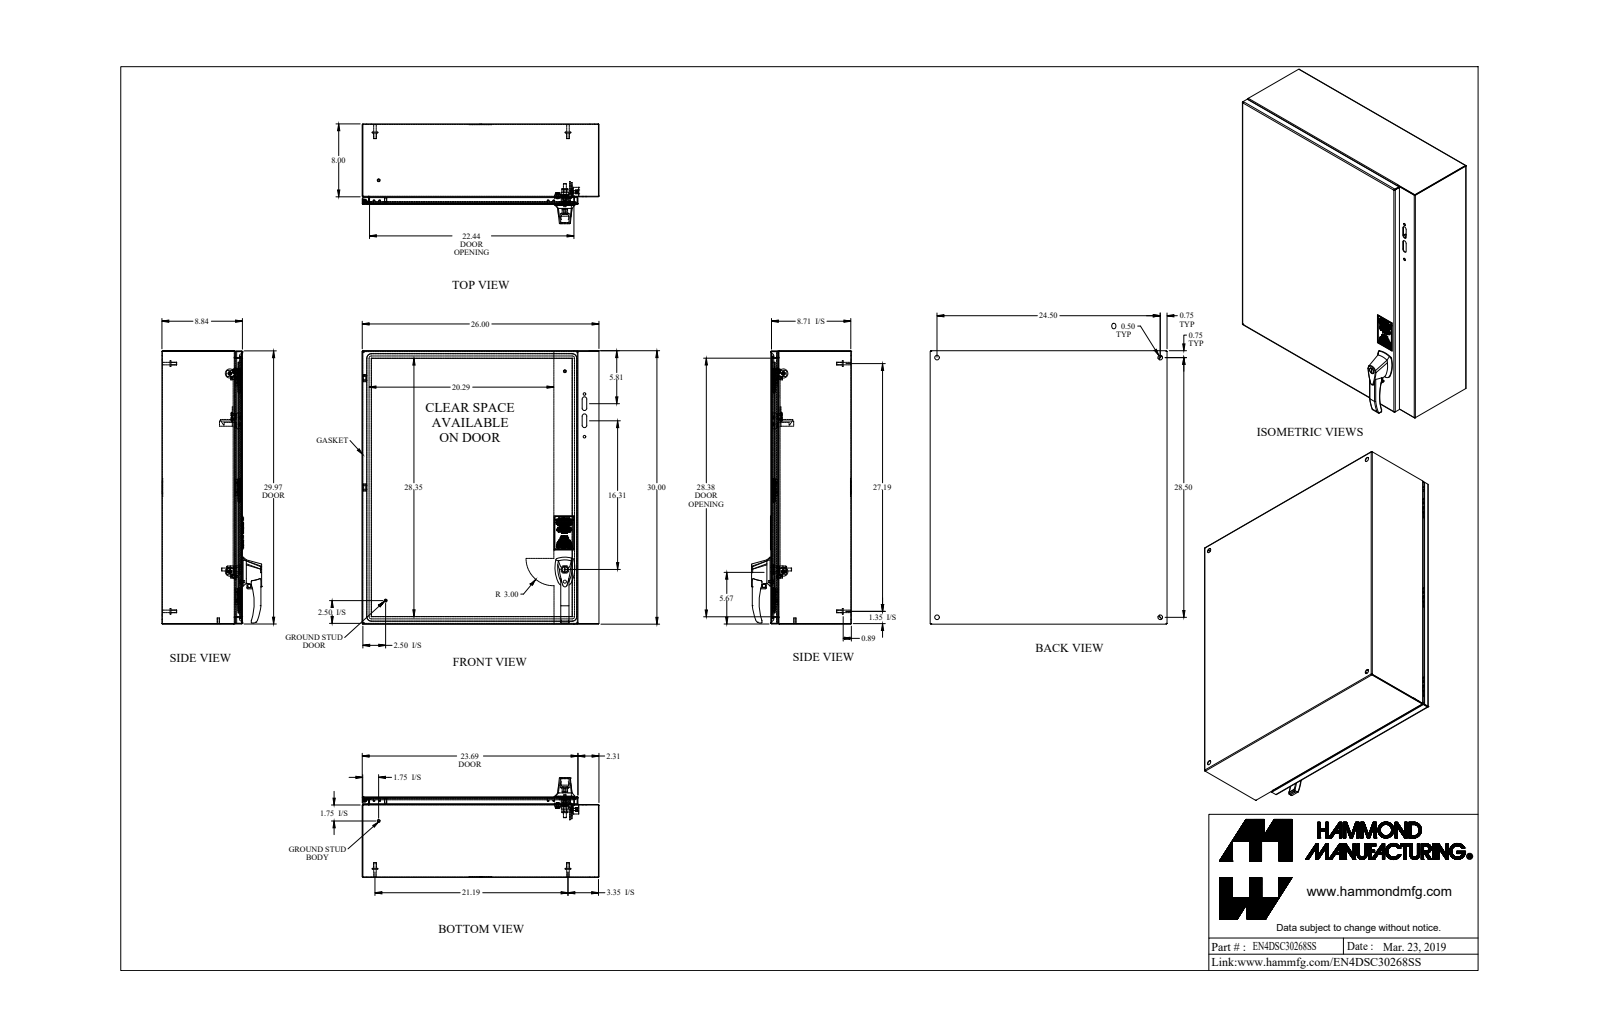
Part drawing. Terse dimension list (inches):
name: EN4DSC30268GY
written by: SolidWorks 2019 (AUTOMOTIVE_DESIGN)
unit: in
bodies: 51 solids, 1065 faces (573 planar, 335 cylindrical, 157 other)
size: 30.016 × 26 × 10.952
volume: 194.4 in³; area: 5 933 in²
holes: 4× ⌀0.176, 2× ⌀0.156, 2× ⌀0.173, 2× ⌀0.215, 2× ⌀0.25, 2× ⌀0.265, 2× ⌀0.281, 2× ⌀0.413, 1× ⌀0.172, 1× ⌀0.196, 1× ⌀0.233, 1× ⌀0.24
bosses: 7× ⌀0.25, 4× ⌀0.375, 4× ⌀0.313, 4× ⌀0.27, 4× ⌀0.156, 2× ⌀1, 2× ⌀0.625, 2× ⌀0.625
rounds: 28× R0.079, 16× R0.022, 14× R0.25, 12× R0.043, 12× R0.081, 11× R0.125, 8× R0.136, 6× R0.006
face distances: 0.057, 8.708, 8.765, 0.072, 8.78, 8.837, 25.943, 29.943, 7.943, 26
hole spacings: 21.75, 1.11, 0.52, 0.75, 0.834, 0.886, 0.998, 1.004
